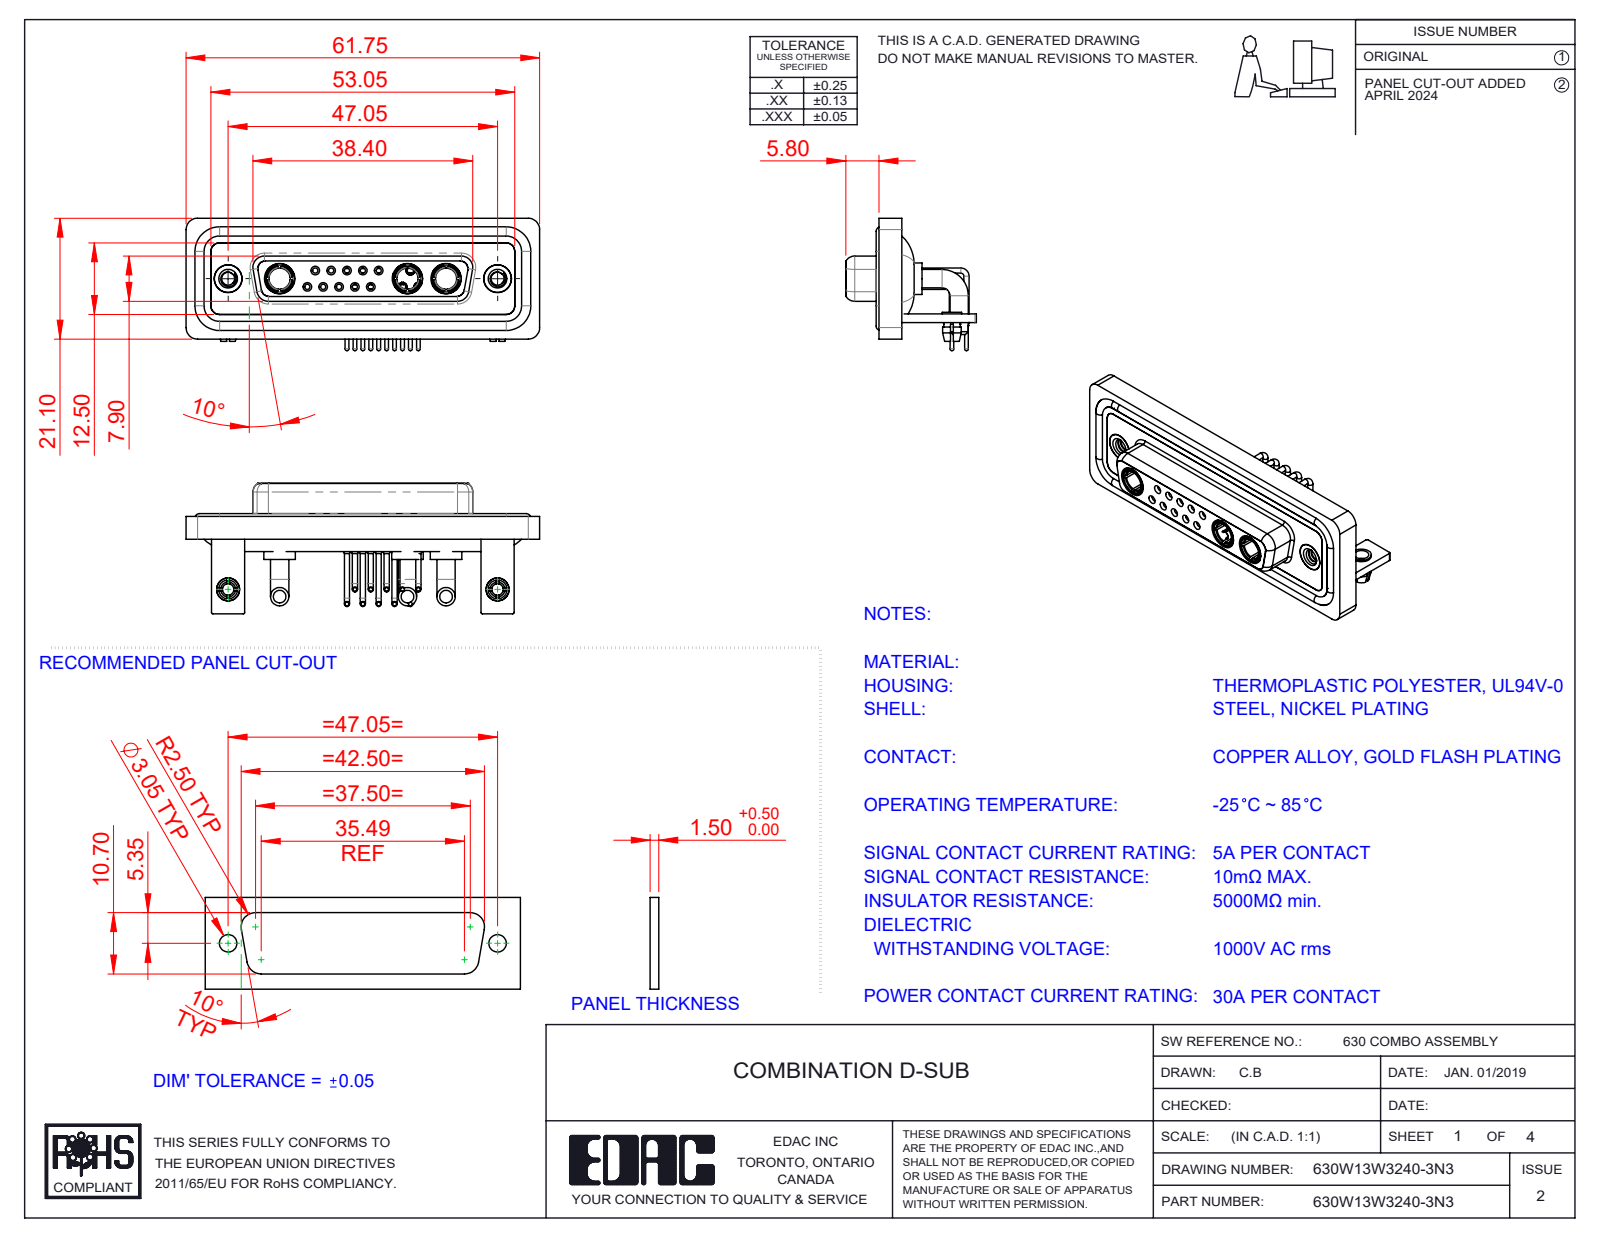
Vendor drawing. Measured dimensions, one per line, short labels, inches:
name: 630Combo Contact Row 1_50 Contacts; 630Combo Shell Front_25 Contacts; 630Combo Waterproof Housing_25 Contacts; 630Combo Board Lock_50 Contacts (+7 more)
written by: SolidWorks 2023 (CONFIG_CONTROL_DESIGN)
unit: in
bodies: 27 solids, 1290 faces (410 planar, 549 cylindrical, 331 other)
size: 2.431 × 0.91 × 0.898
volume: 0.547 in³; area: 23.71 in²
holes: 12× ⌀0.079, 10× ⌀0.035, 10× ⌀0.043, 10× ⌀0.059, 5× ⌀0.063, 5× ⌀0.067, 5× ⌀0.191, 3× ⌀0.146, 3× ⌀0.209, 2× ⌀0.089, 2× ⌀0.098, 2× ⌀0.126
bosses: 15× ⌀0.035, 12× ⌀0.063, 10× ⌀0.026, 6× ⌀0.126, 5× ⌀0.079, 5× ⌀0.059, 3× ⌀0.217, 3× ⌀0.205
rounds: 19× R0.079, 18× R0.059, 16× R0.01, 8× R0.053, 8× R0.063, 5× R0.02, 4× R0.024, 4× R0.026
face distances: 0.016, 0.071, 0.114, 0.146, 0.059, 0.161, 0.043, 0.055, 0.063, 0.122
hole spacings: 0.124, 0.109, 0.218, 0.198, 0.327, 0.198, 0.295, 0.436
